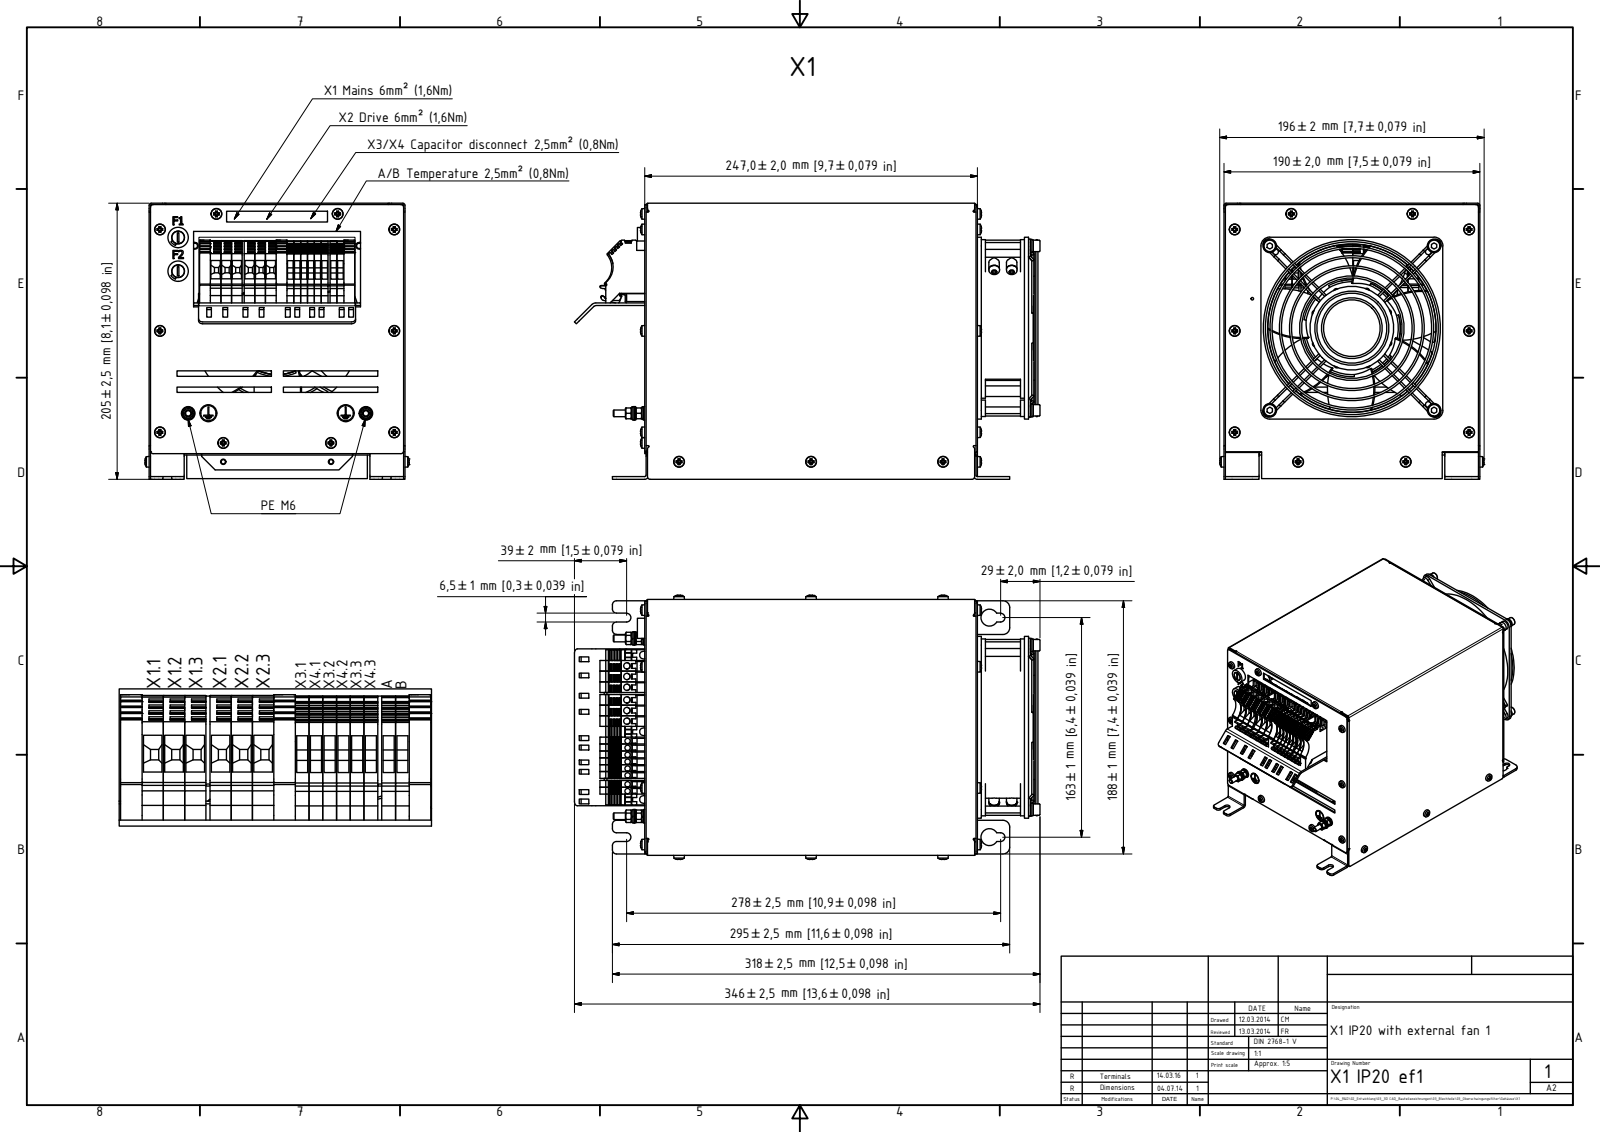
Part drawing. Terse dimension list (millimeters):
name: 10100282 Bodenblech RHF-BG X1; 10100383 Deckel RHF-BG X1-A; 10100382 Anschlussblech RHF-BG X1; 10100363 Lüfterblech RHF-BG X1 (+8 more)
written by: Autodesk Inventor 2015 (AUTOMOTIVE_DESIGN)
unit: mm
bodies: 104 solids, 8036 faces (5035 planar, 2077 cylindrical, 924 other)
size: 345.64 × 205 × 196.23
volume: 695 055 mm³; area: 829 571 mm²
holes: 21× ⌀5, 19× ⌀4, 15× ⌀3.24, 12× ⌀4.72, 8× ⌀3.5, 8× ⌀6, 7× ⌀4.2, 6× ⌀5.3, 6× ⌀5.4, 4× ⌀6.5, 4× ⌀12.5, 3× ⌀5.6
bosses: 24× ⌀1.5, 19× ⌀4, 15× ⌀3.65, 8× ⌀9.2, 6× ⌀10, 6× ⌀5, 4× ⌀8.5, 4× ⌀7.74
rounds: 58× R0.5, 47× R2, 39× R1, 32× R0.15, 30× R0.75, 30× R3, 29× R0.1, 24× R0.45
face distances: 1, 189, 2, 246, 188, 190, 245, 184, 185, 186
hole spacings: 5.1, 23.56, 10.2, 23, 25.16, 122.16, 15.3, 27.62
